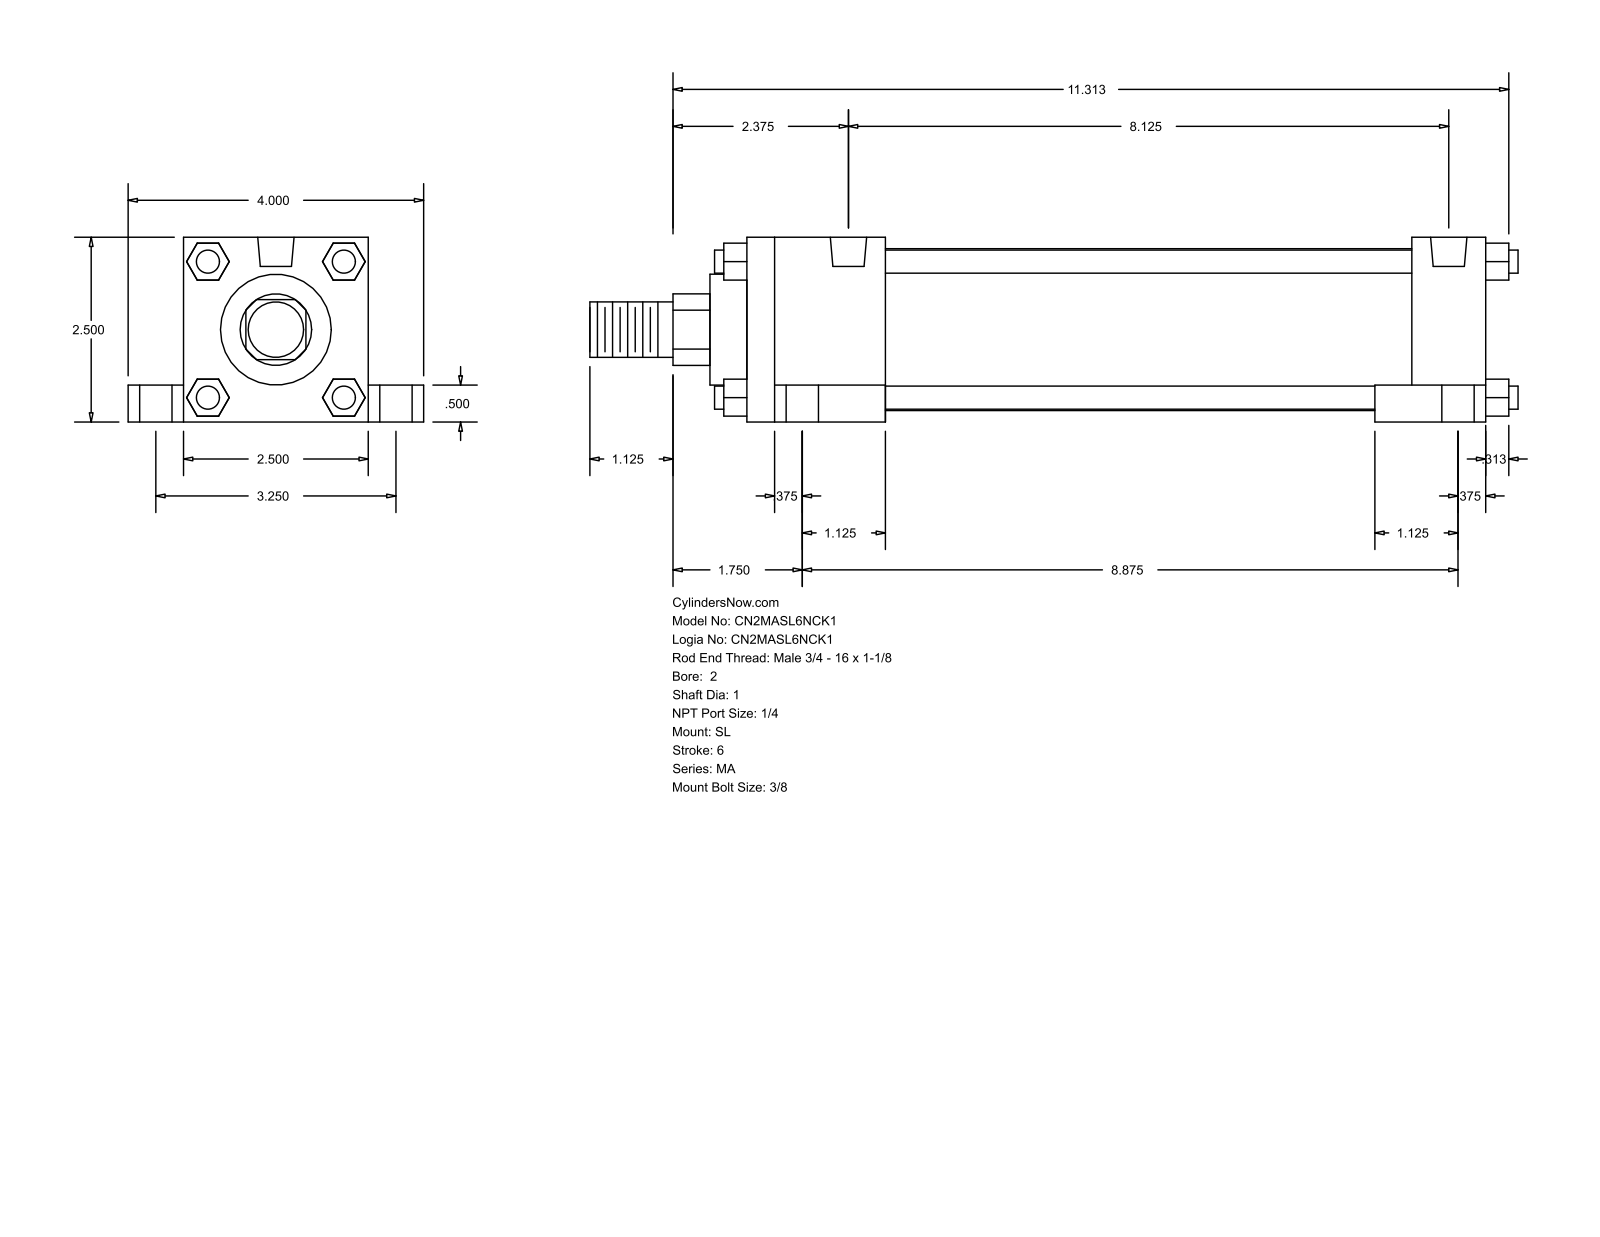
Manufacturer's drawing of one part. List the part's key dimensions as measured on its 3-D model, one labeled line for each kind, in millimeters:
Part name (STEP PRODUCT): MA_SL__0200_1
STEP written by: GSSL Pune (CONFIG_CONTROL_DESIGN)
Units: millimetres
Bodies: 0 solids, 148 faces (112 planar, 36 cylindrical, 0 other)
Overall size (bounding box): 319.09 × 101.6 × 63.5
Round holes (diameter × count): ⌀7.94 ×4, ⌀11.11 ×4, ⌀17.46 ×4, ⌀12.49 ×2
Round bosses / shafts (diameter × count): ⌀7.94 ×4, ⌀55.63 ×1, ⌀38.1 ×1, ⌀25.4 ×1, ⌀19.05 ×1
Partial cylindrical surfaces — rounded edges, fillets, slot ends (radius × count): R12.29 ×1
Main face-to-face distances: 63.5, 12.7, 254, 19.05, 82.55, 25.4, 50.8, 47.63, 206.37, 228.6
Hole centre spacings: 41.39, 44.22, 82.54, 206.37, 213.58, 225.43, 226.05, 240.07
